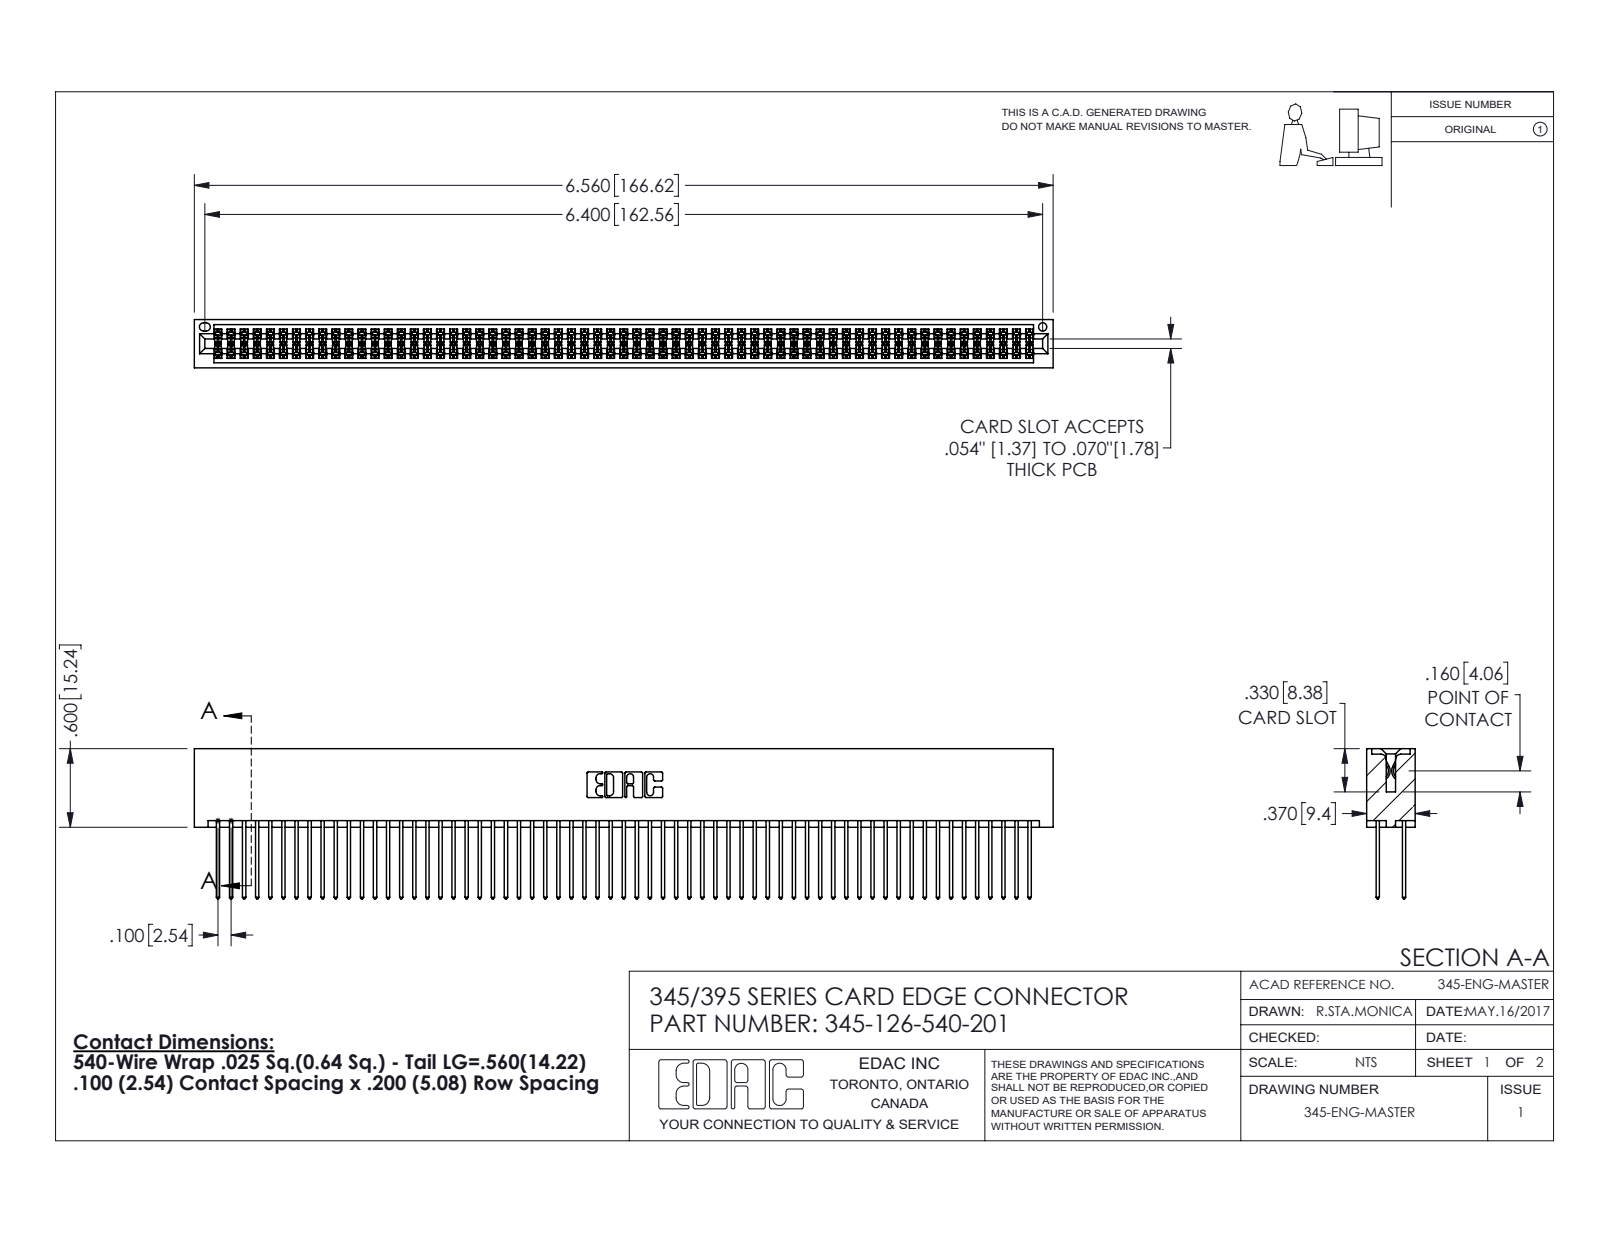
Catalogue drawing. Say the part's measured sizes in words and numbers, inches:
The part is named "345-126-540-201; 345 Part_No Mounting Lugs; 345-292-001_345-293-140". Its 3-D file was written by "SolidWorks 2016 (CONFIG_CONTROL_DESIGN)". It is 127 solids with 6418 faces: 4234 planar, 2184 cylindrical and 0 other. Overall it measures 6.56 by 1.147 by 0.37 inches. Its volume is 1.066 cubic inches and its surface area 44.57 square inches. Round holes: 1 of diameter 0.064. Partial cylindrical surfaces (rounded edges, fillets, slot ends): 189 of radius 0.006, 126 of radius 0.01, 22 of radius 0.01, 6 of radius 0.007, 6 of radius 0.031, 3 of radius 0.026, 2 of radius 0.014, 2 of radius 0.019. The main face-to-face distances are 0.298, 0.072, 0.2, 0.098, 0.272, 0.025, 0.225, 0.37, 0.175, 0.149.
